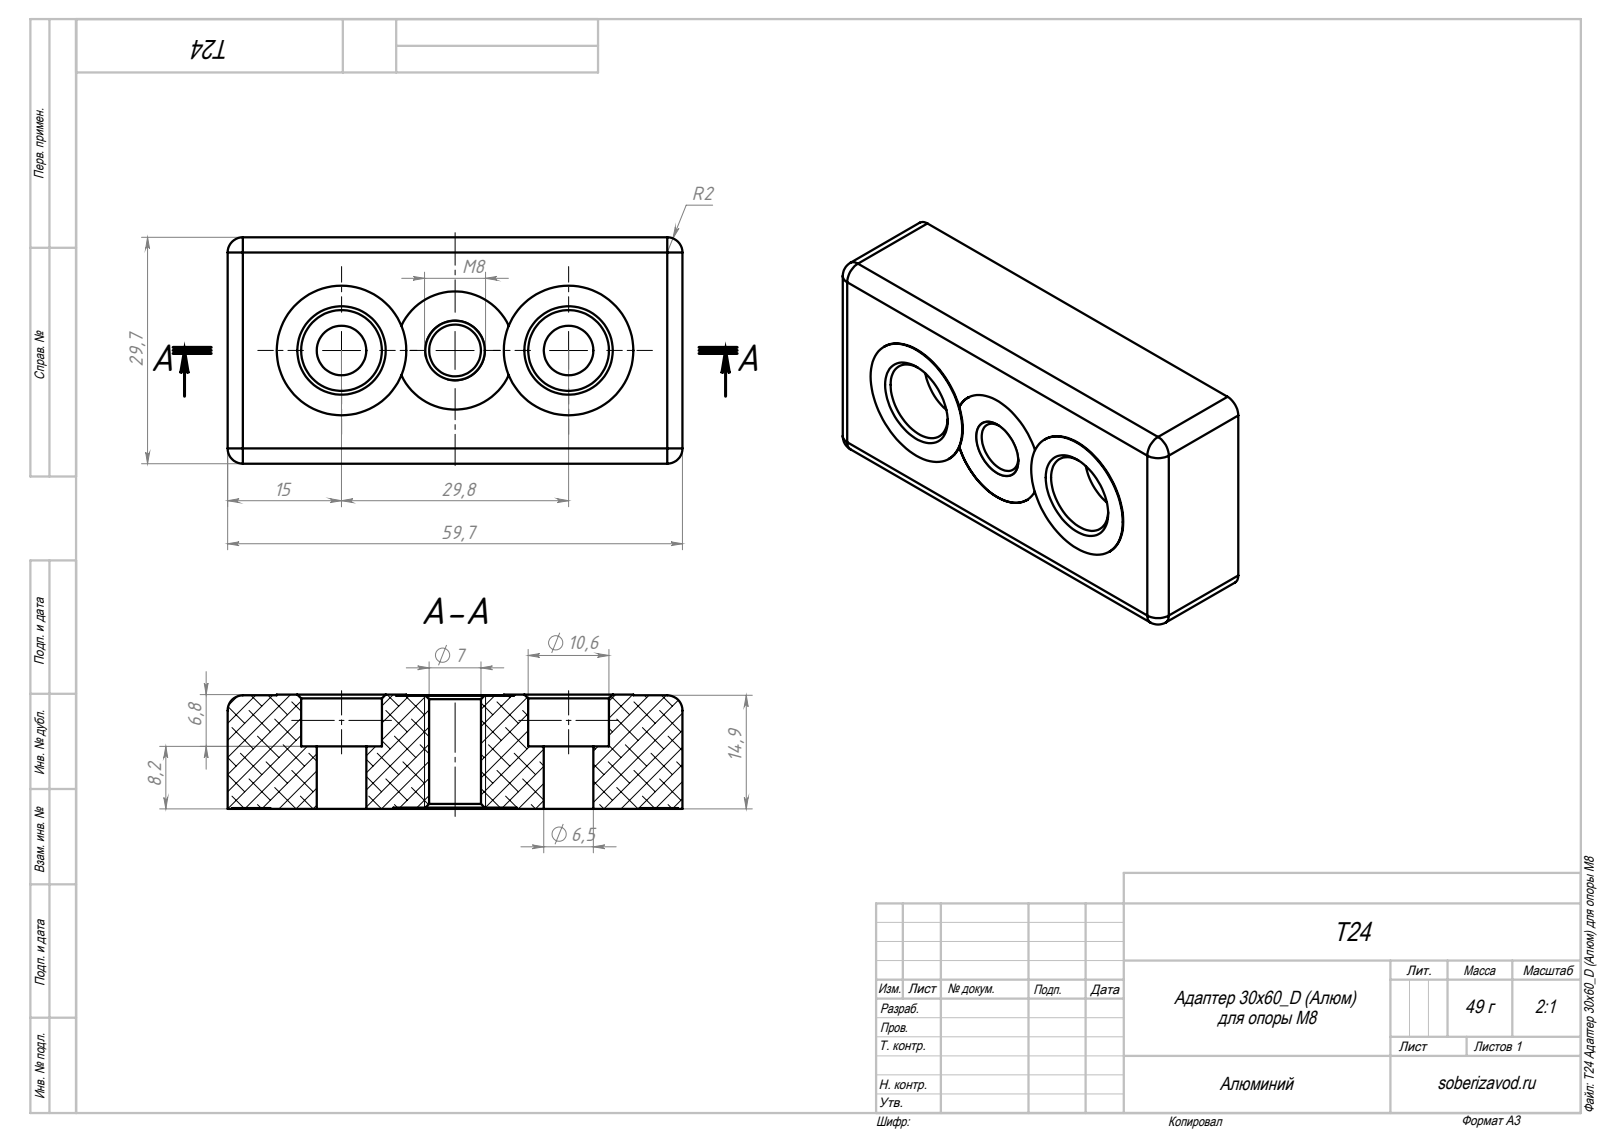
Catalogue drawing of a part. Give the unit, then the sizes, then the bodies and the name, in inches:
Units: inches
Overall size (bounding box): 2.35 × 1.169 × 0.591
Round holes (diameter × count): ⌀0.197 ×2, ⌀0.256 ×2, ⌀0.417 ×2, ⌀0.276 ×1, ⌀0.61 ×1, ⌀0.638 ×1
Round bosses / shafts (diameter × count): ⌀0.197 ×6, ⌀0.669 ×2
Partial cylindrical surfaces — rounded edges, fillets, slot ends (radius × count): R0.079 ×8, R0.372 ×3
Main face-to-face distances: 0.114, 0.587, 1.055, 1.169, 0.941, 2.236, 0.472, 2.35, 0.469, 0.583
Hole centre spacings: 0.467, 0.587, 1.053, 1.64, 1.173, 2.106
Volume: 1.147 in³ · Surface area: 16.08 in²
Bodies: 1 solid, 161 faces (72 planar, 85 cylindrical, 4 other)
STEP written by: SolidWorks 2018 (AUTOMOTIVE_DESIGN)
